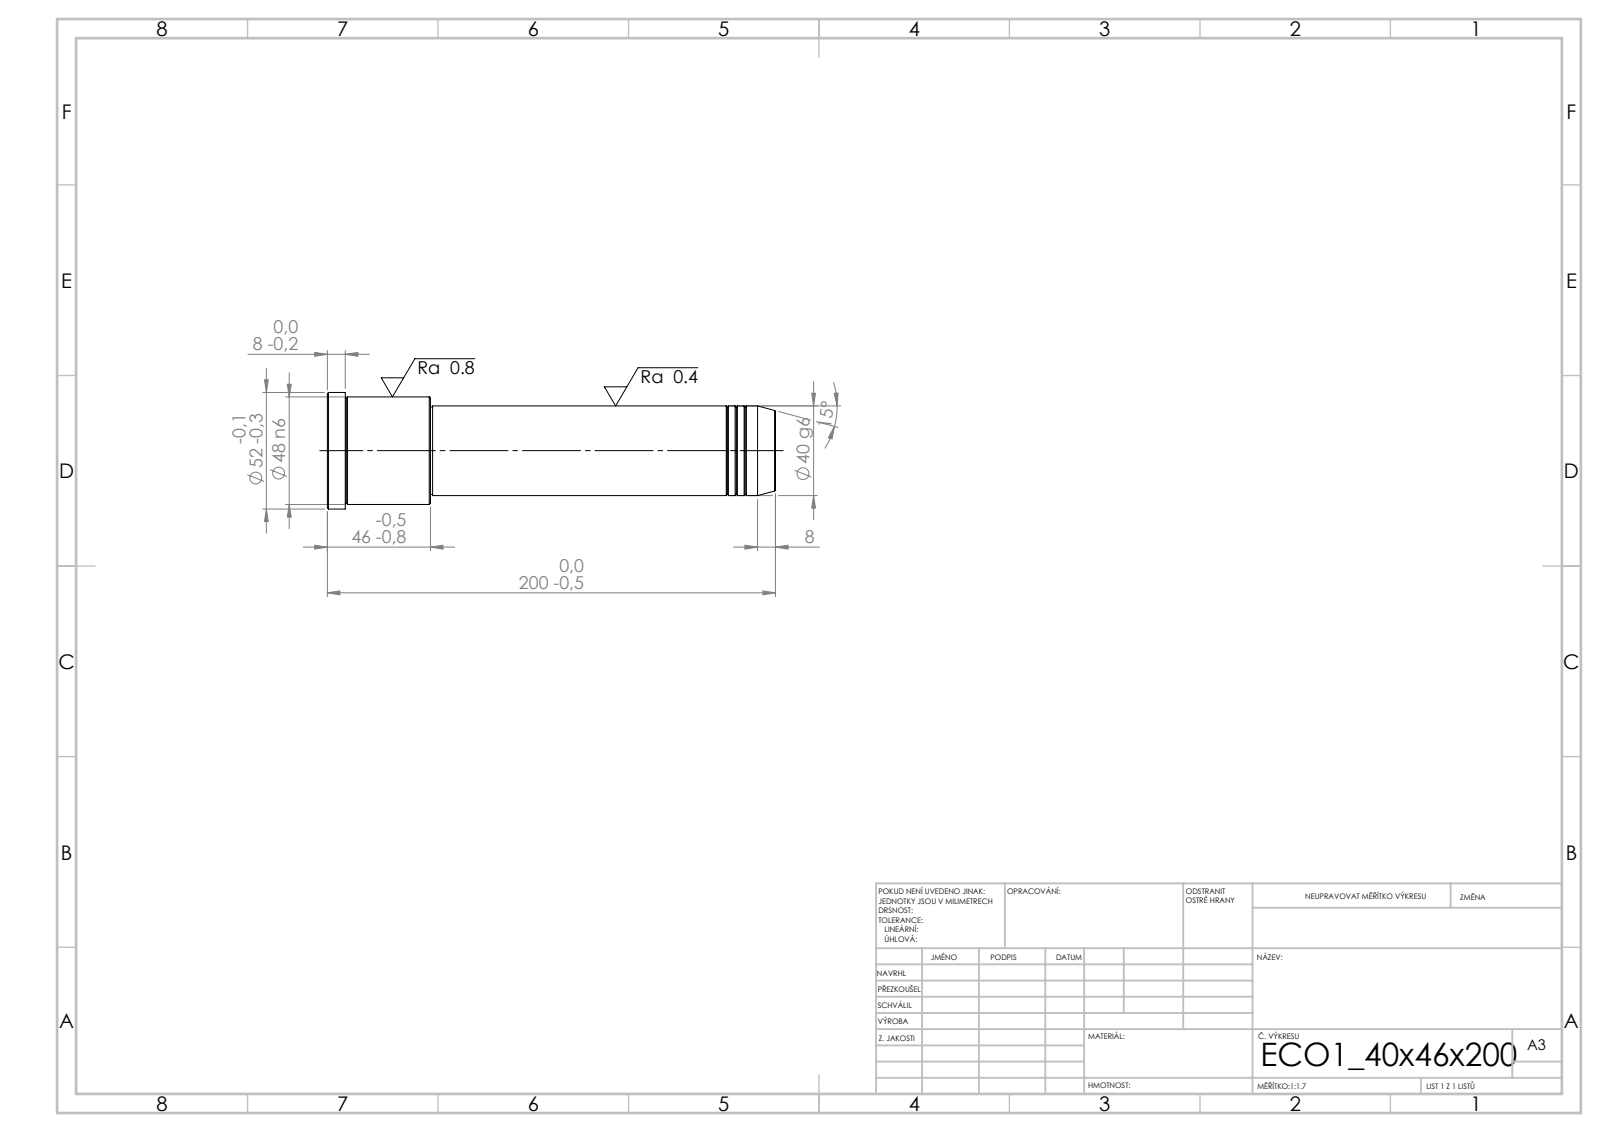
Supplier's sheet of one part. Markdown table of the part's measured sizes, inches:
| quantity | value |
| --- | --- |
| STEP written by | SolidWorks 2019 (CONFIG_CONTROL_DESIGN) |
| units | inches |
| bodies | 1 solid, 43 faces (5 planar, 14 cylindrical, 24 other) |
| overall size | 7.874 × 2.047 × 2.047 |
| volume | 16.96 in³ |
| surface area | 47.53 in² |
| round bosses / shafts (diameter × count) | 2.047 × 1, 1.89 × 1, 1.575 × 1, 1.535 × 1 |
| main face-to-face distances | 7.874, 6.063, 1.811, 7.559, 1.496, 0.315, 6.024, 0.039, 1.535, 1.85 |
